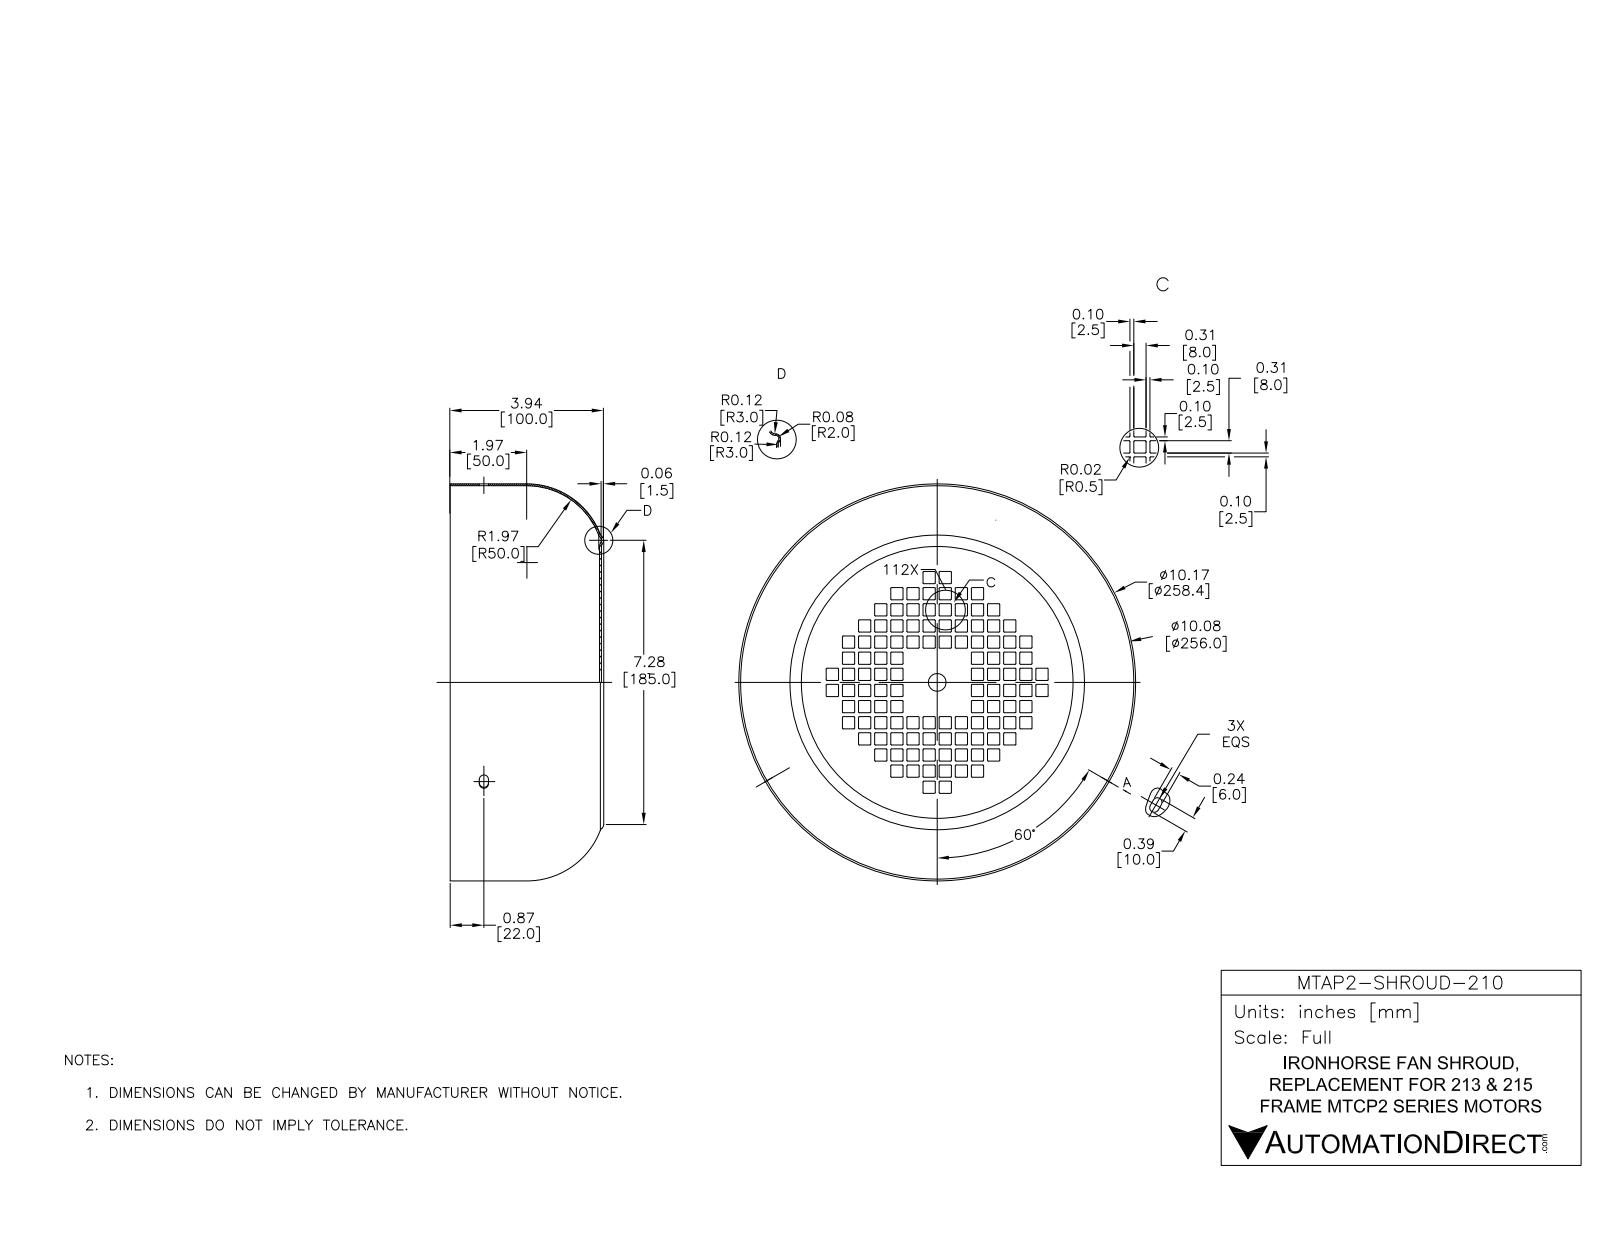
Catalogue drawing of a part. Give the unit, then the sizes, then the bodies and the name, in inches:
Units: inches
Overall size (bounding box): 10.173 × 10.173 × 3.937
Round holes (diameter × count): ⌀0.453 ×1, ⌀10.079 ×1
Round bosses / shafts (diameter × count): ⌀10.173 ×1
Partial cylindrical surfaces — rounded edges, fillets, slot ends (radius × count): R0.118 ×6
Main face-to-face distances: 0.047, 0.039, 0.394, 0.787, 1.181, 1.575, 0.315, 1.969, 0.709, 0.079
Volume: 7.972 in³ · Surface area: 363.2 in²
Bodies: 1 solid, 601 faces (570 planar, 15 cylindrical, 16 other)
Part name (STEP PRODUCT): MTAP2-SHROUD-210
STEP written by: SolidWorks 2017 (AUTOMOTIVE_DESIGN)
